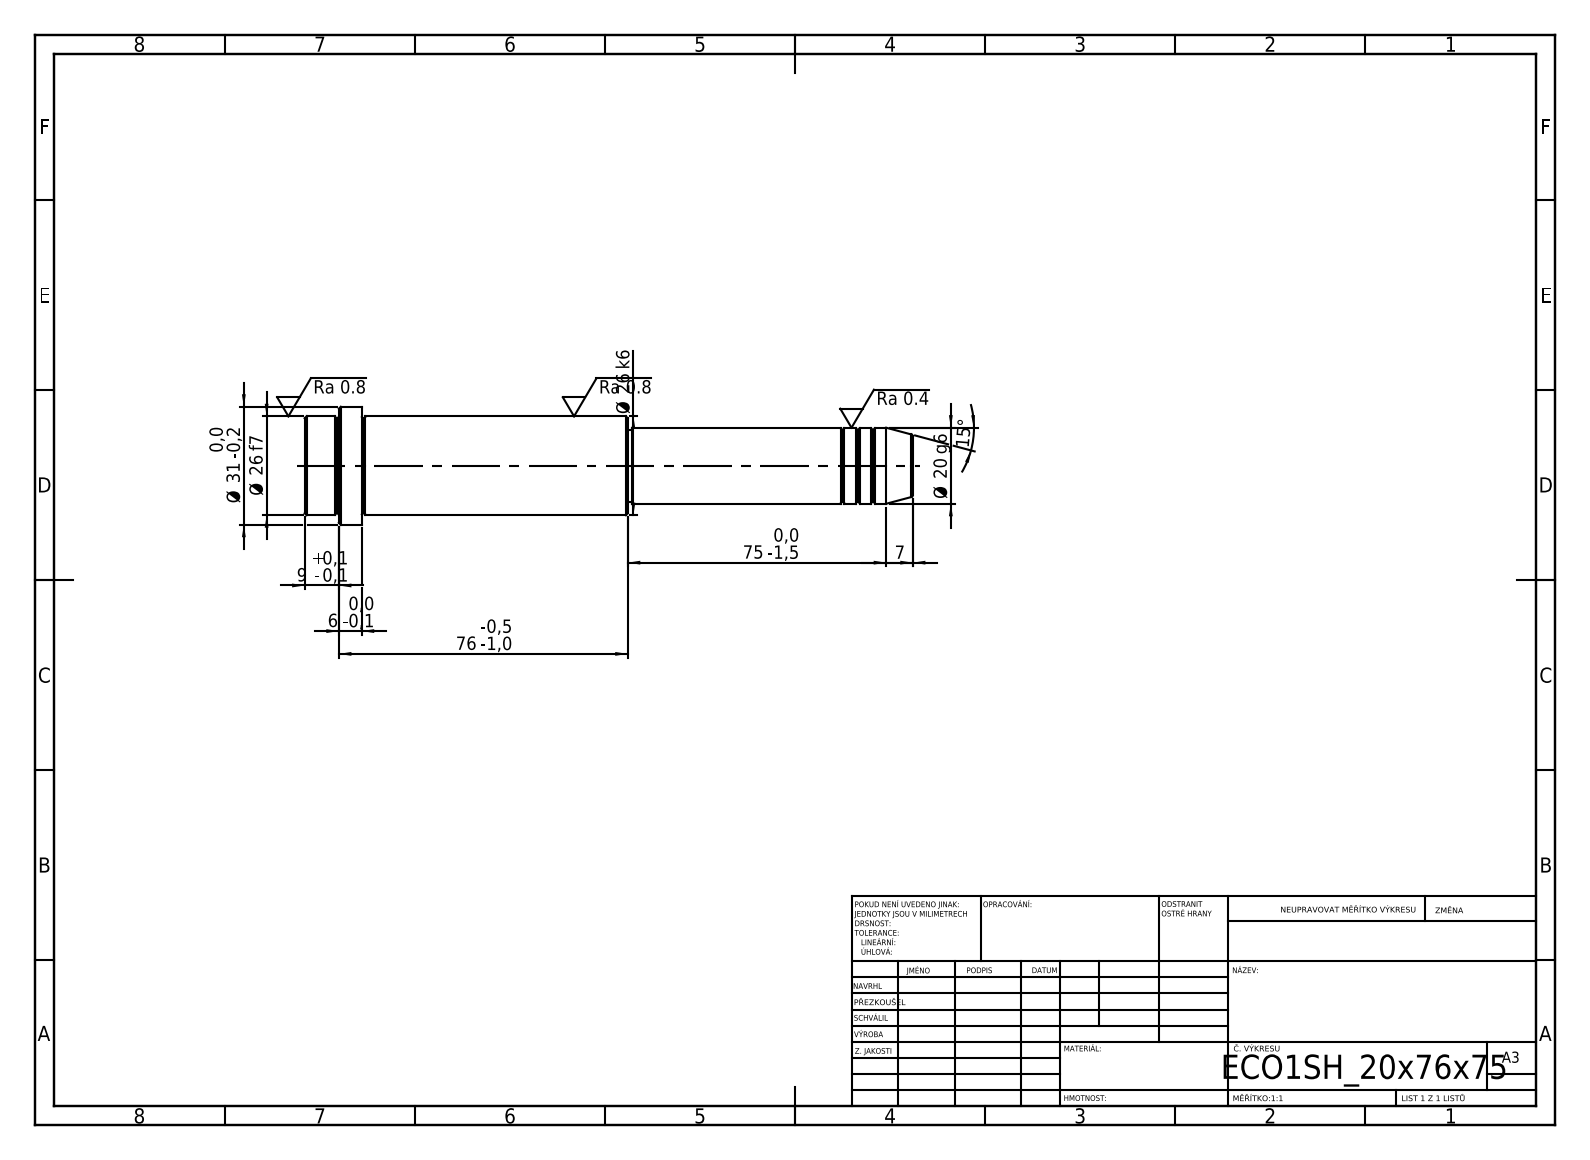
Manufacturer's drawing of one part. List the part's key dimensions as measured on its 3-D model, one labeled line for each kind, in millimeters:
STEP written by: SolidWorks 2019 (CONFIG_CONTROL_DESIGN)
Units: millimetres
Bodies: 1 solid, 52 faces (6 planar, 16 cylindrical, 30 other)
Overall size (bounding box): 160 × 31 × 31
Volume: 69 447 mm³ · Surface area: 13 285 mm²
Round bosses / shafts (diameter × count): ⌀31 ×1, ⌀26 ×1, ⌀20 ×1, ⌀19 ×1
Main face-to-face distances: 15, 70, 85, 75, 145, 160, 151, 76, 6, 9
